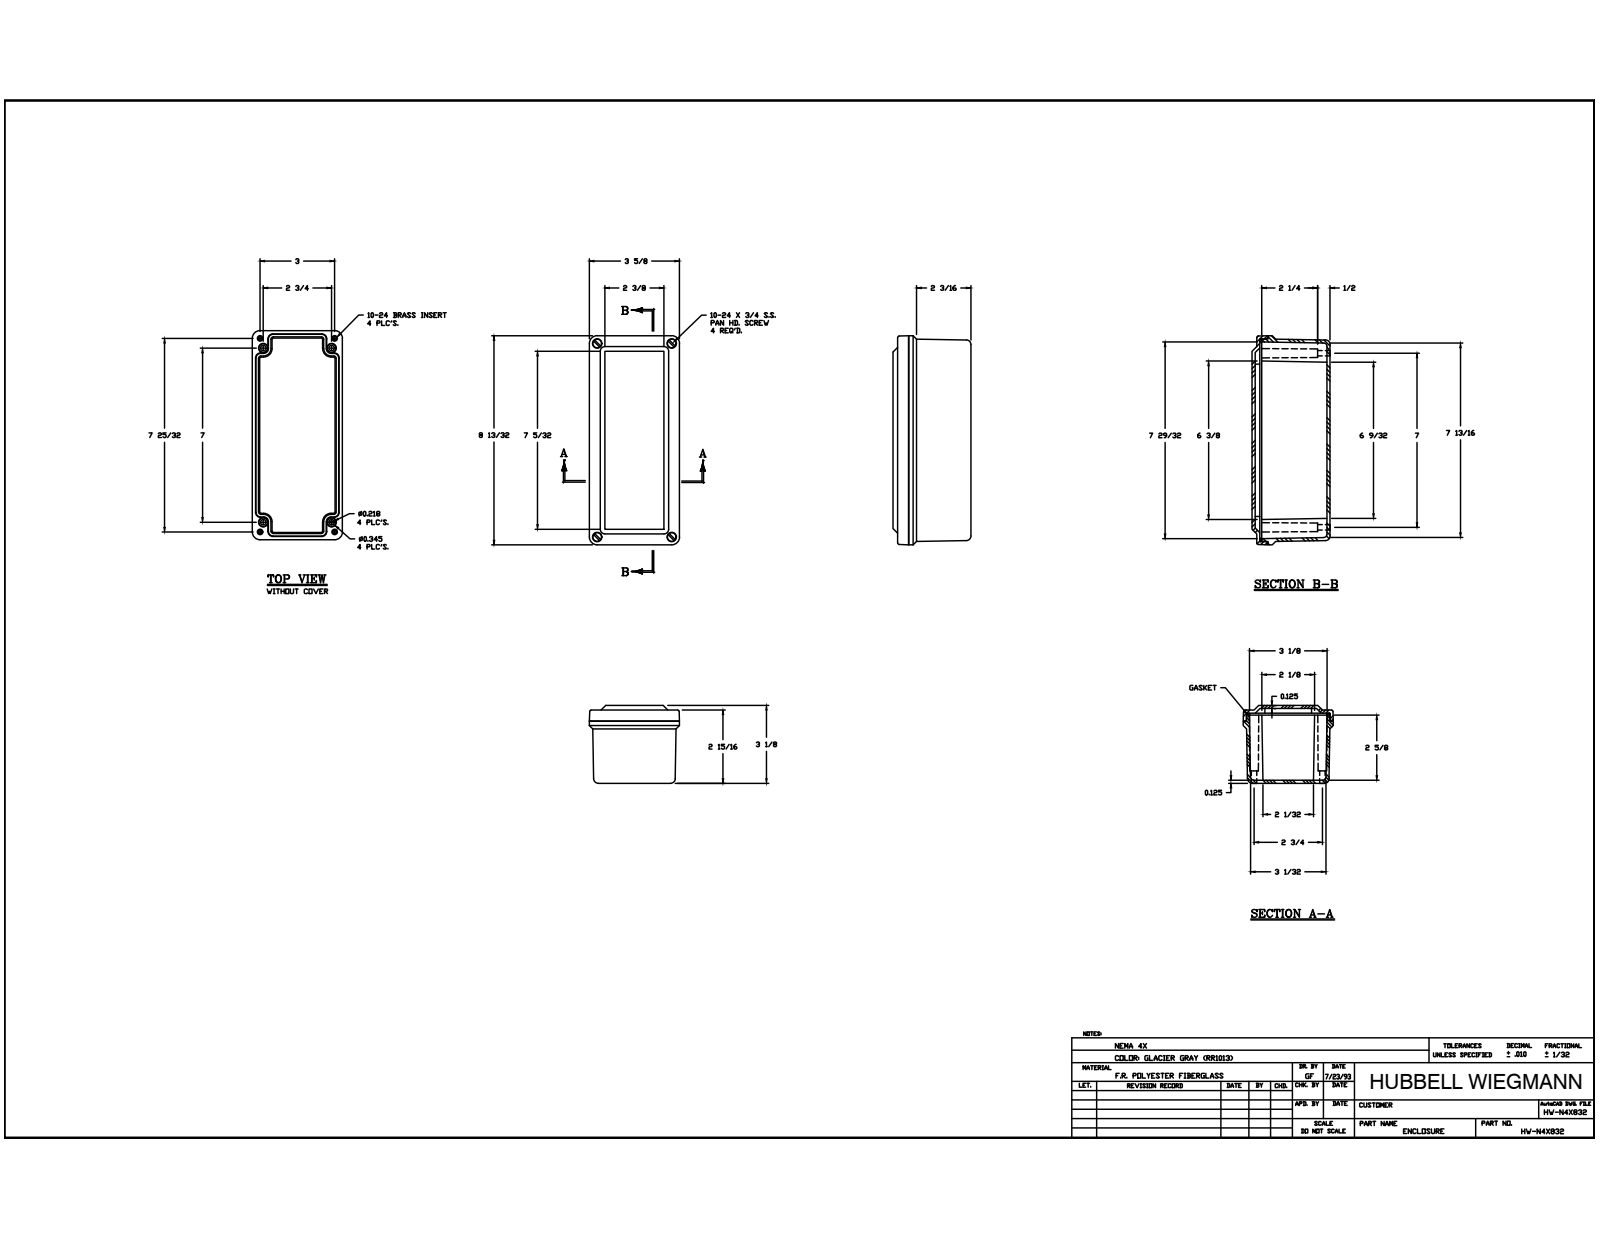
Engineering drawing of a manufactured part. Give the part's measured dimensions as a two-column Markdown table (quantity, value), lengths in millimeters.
| quantity | value |
| --- | --- |
| part name | 10-24 X 0.4375 DP BRASS INSERT; 10-24x0.75 DP combo screw; WPCF832 BOX; WPCF832 GASKET (+3 more) |
| STEP written by | Autodesk Inventor 2014 (AUTOMOTIVE_DESIGN) |
| units | millimeters |
| bodies | 11 solids, 375 faces (167 planar, 112 cylindrical, 96 other) |
| overall size | 213.6 × 92.08 × 79.38 |
| volume | 306 515 mm³ |
| surface area | 178 711 mm² |
| round holes (diameter × count) | 5.56 × 8, 3.68 × 4, 4.83 × 4, 9.52 × 4 |
| round bosses / shafts (diameter × count) | 9.42 × 4, 5.54 × 4, 4.5 × 4 |
| partial cylindrical surfaces (radius × count) | 0.79 × 20, 0.3 × 16, 1.22 × 8, 1.59 × 4, 4.47 × 4, 4.76 × 4, 5.59 × 4, 7.94 × 4 |
| main face-to-face distances | 3.17, 3.09, 76.2, 4.76, 79.37, 73.03, 71.44, 1.59, 68.27, 7.93 |
| hole center spacings | 10.42, 73.69, 187.75, 201.42, 69.84, 76.2, 177.8, 191.02 |
